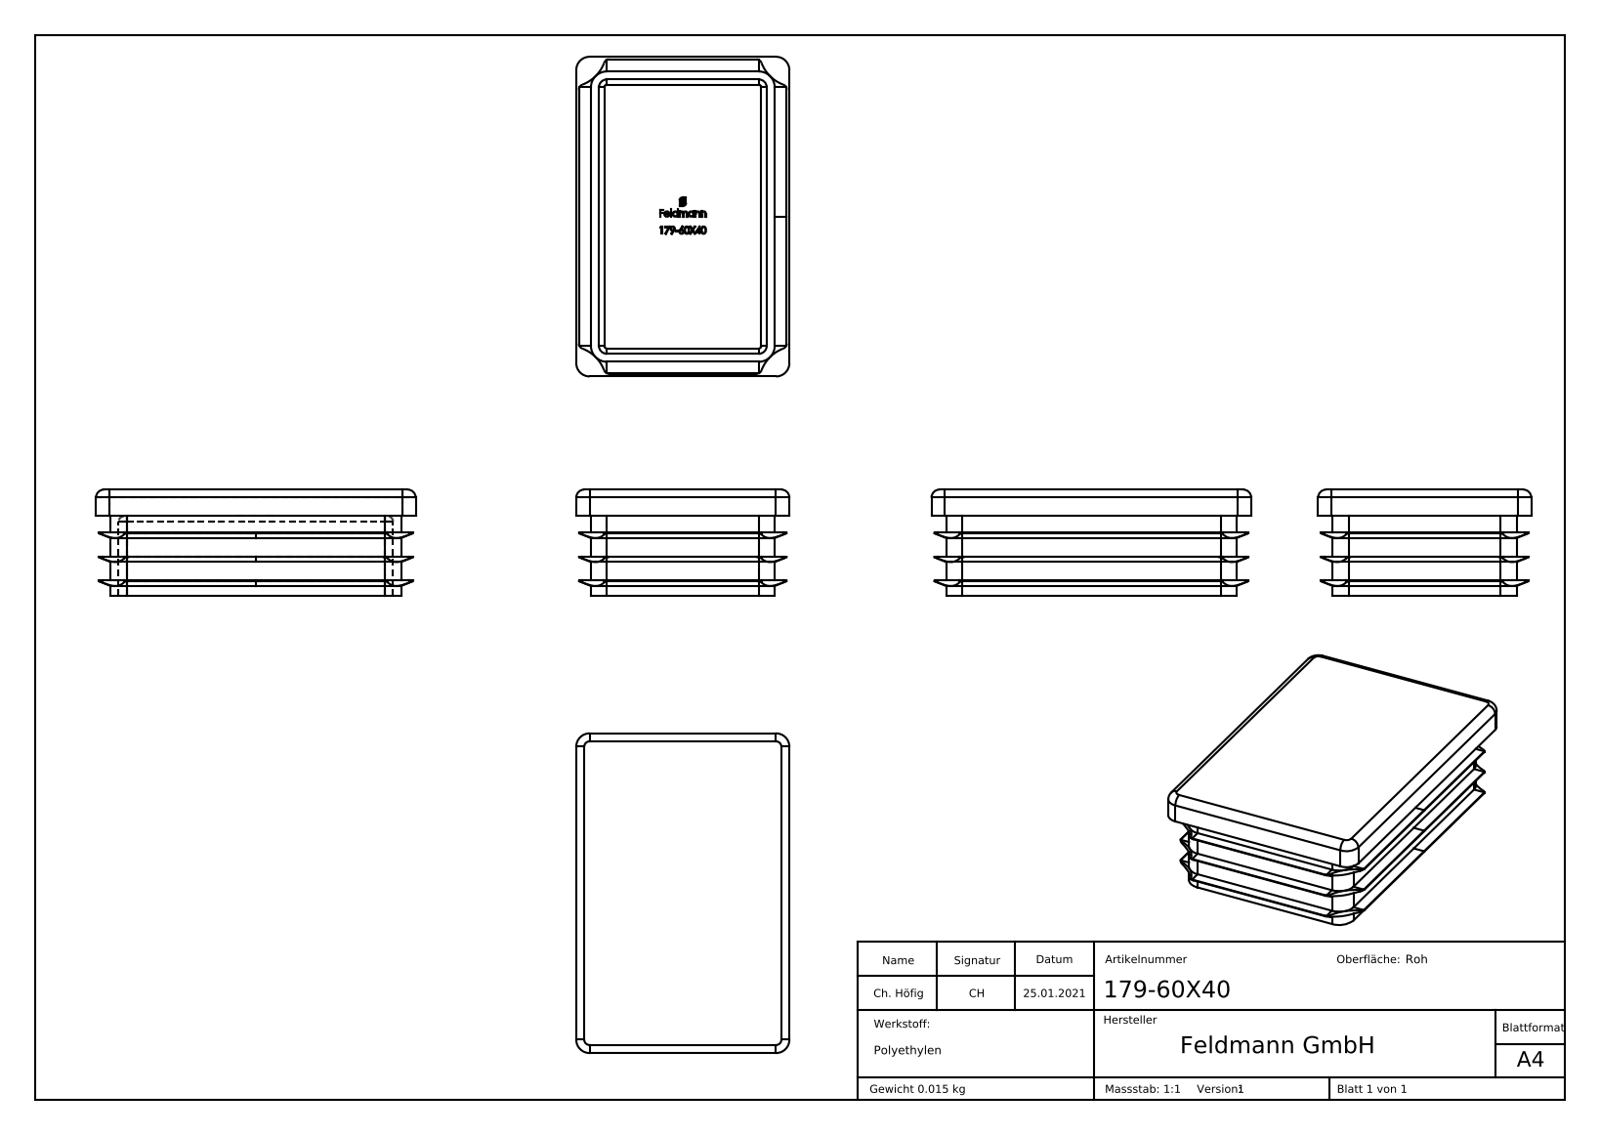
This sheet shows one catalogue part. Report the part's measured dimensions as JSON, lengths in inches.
{"part_name": "179-60X40", "step_written_by": "SolidWorks 2018 (CONFIG_CONTROL_DESIGN)", "units": "inches", "bodies": {"solids": 1, "faces": 448, "planar": 229, "cylindrical": 83, "other": 136}, "overall_size": [2.362, 1.575, 0.787], "volume_in3": 0.994, "surface_area_in2": 19.29, "partial_cylinders_radius": [[0.039, 12], [0.059, 8], [0.098, 4], [0.118, 4], [0.276, 4]], "face_to_face_distances": [0.197, 0.059, 1.299, 0.177, 2.087, 1.24, 0.108, 0.167, 1.358, 2.028]}
